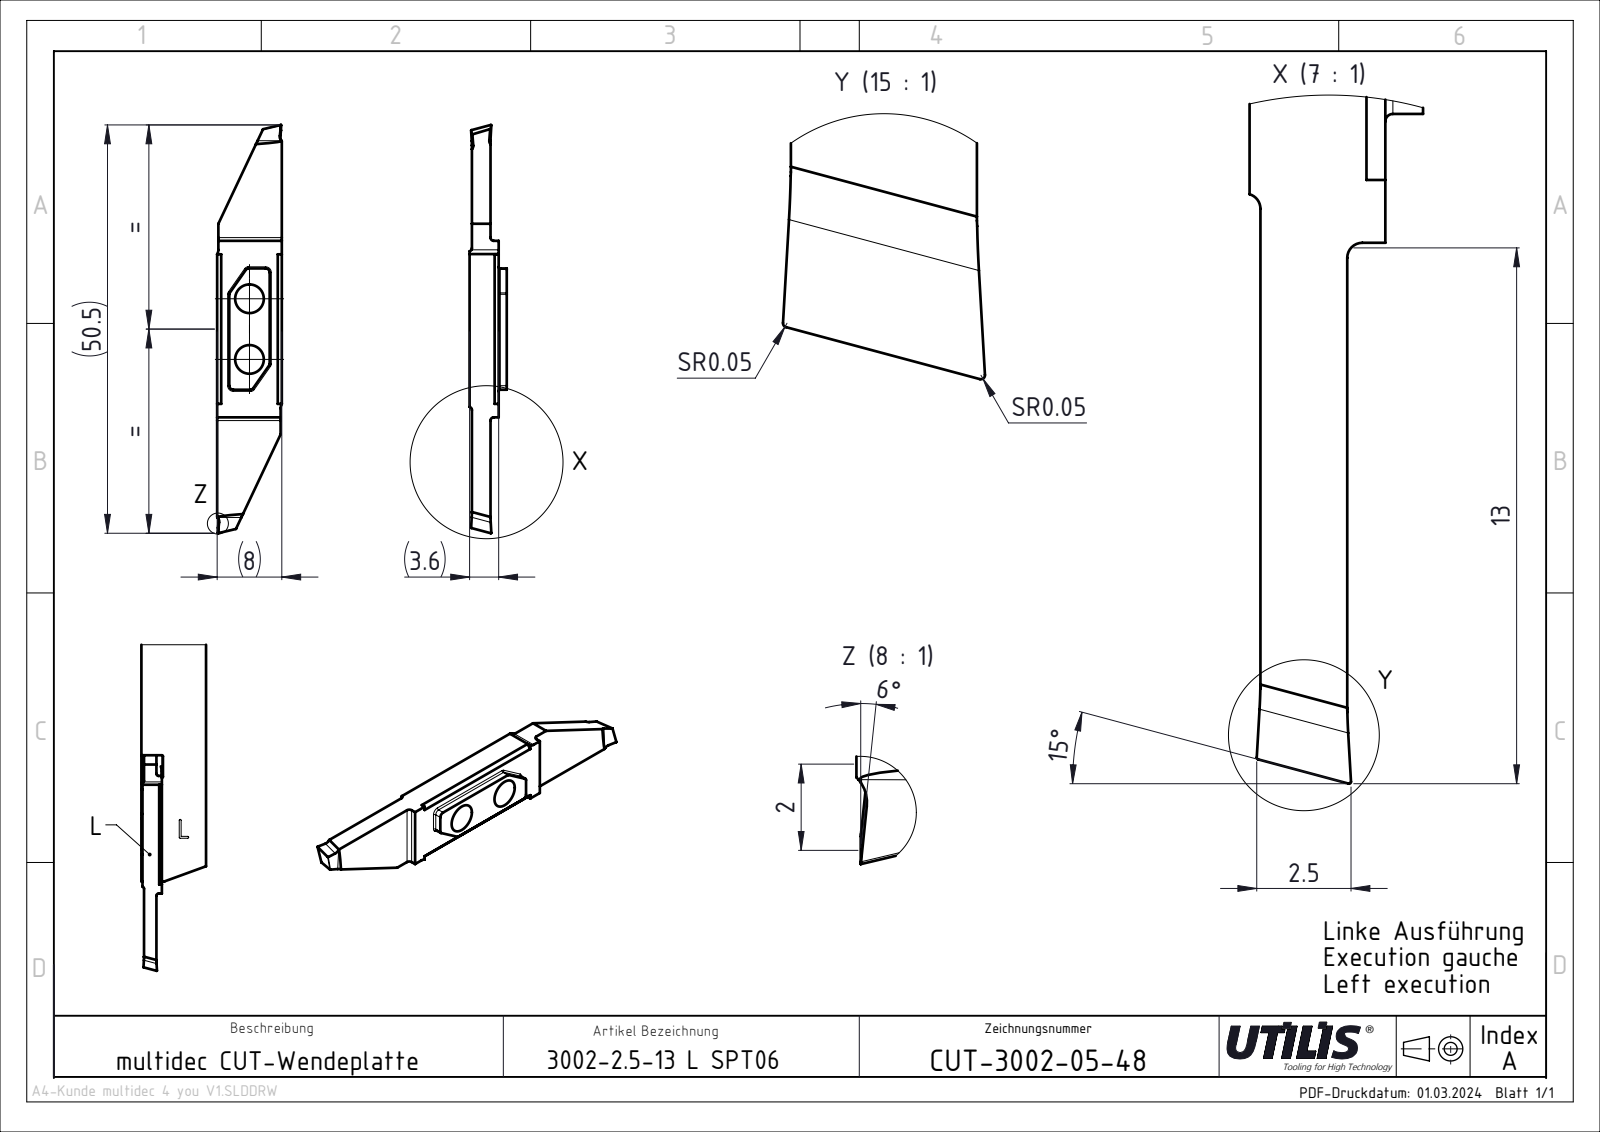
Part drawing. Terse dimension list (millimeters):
name: CUT-3002 SPT Slim_and_Deep; ASME Y14.5
written by: SolidWorks 2023 SP4 || FormatWorks Professional (AP242_MANAGED_MODEL_BASED_3D_ENGINEERING_MIM_LF)
unit: mm
bodies: 1 solid, 40 faces (26 planar, 14 cylindrical, 0 other)
size: 50.5 × 8 × 3.6
volume: 900 mm³; area: 1 003 mm²
holes: 2× ⌀3.55
rounds: 4× R0.4, 2× R1
face distances: 2.3, 3.31, 1.01, 2.59, 3.6, 8, 18.09, 7.85, 7.7, 21.82
hole spacings: 7.5
